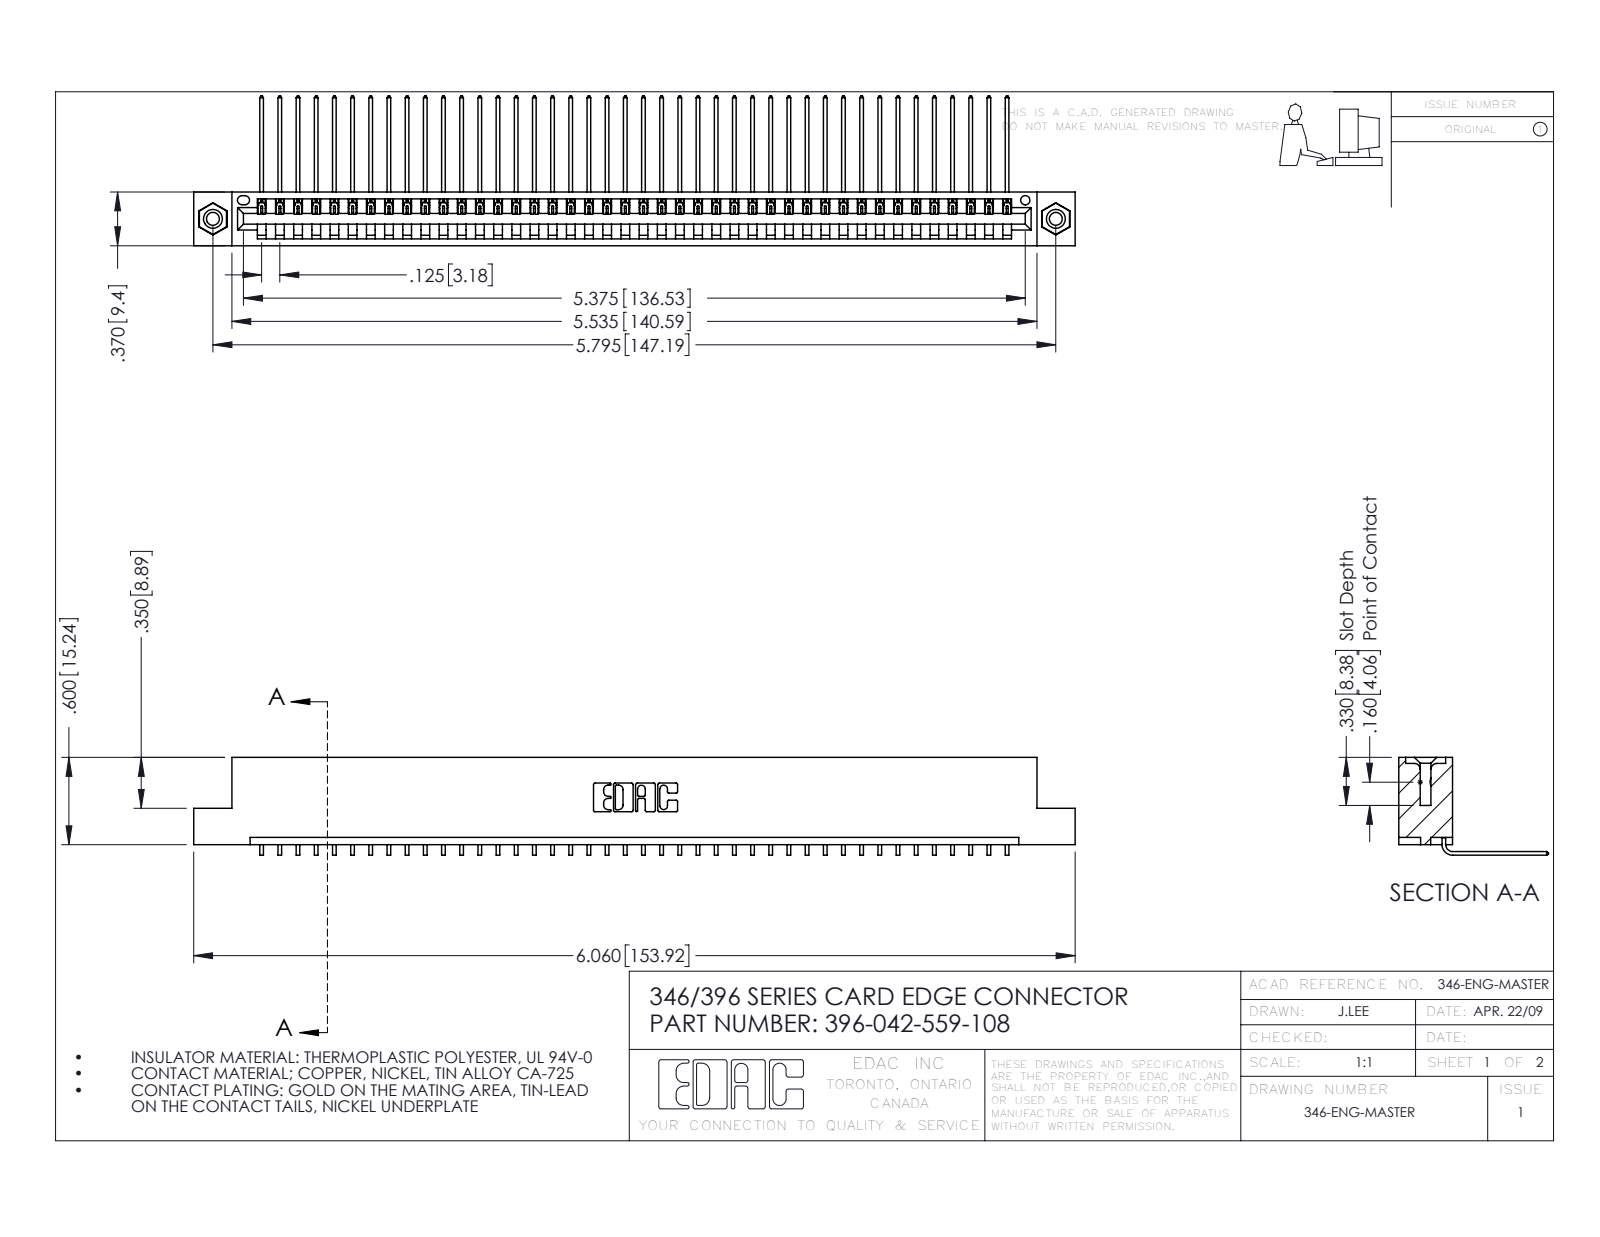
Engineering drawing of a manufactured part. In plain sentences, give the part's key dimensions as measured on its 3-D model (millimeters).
The part is named "396-042-559-108; 345-250-001_345-250-003-102; 346 Part_Flush Mounting Lugs - 0.156 Dia-TI; 345-292-001_558 559 Tail - 1". Its 3-D file was written by "SolidWorks 2016 (CONFIG_CONTROL_DESIGN)". It is 45 solids with 2702 faces: 1872 planar, 814 cylindrical and 16 other. Overall it measures 153.9 by 26.2 by 17.1 millimeters. Its volume is 14 900 cubic millimeters and its surface area 19 440 square millimeters. Round holes: 2 of diameter 2.3, 2 of diameter 3.2, 2 of diameter 4, 1 of diameter 1.6. Round bosses or shafts: 2 of diameter 3.9. Partial cylindrical surfaces (rounded edges, fillets, slot ends): 84 of radius 0.2, 22 of radius 0.3, 6 of radius 0.2, 6 of radius 0.8, 3 of radius 0.7, 2 of radius 0.8, 2 of radius 1, 1 of radius 0.4. The main face-to-face distances are 1.2, 8.2, 9.4, 0.6, 6.4, 1.8, 7.6, 3.8, 5.6, 2.5. The hole center spacings are 6.2, 141.9, 147.2.
